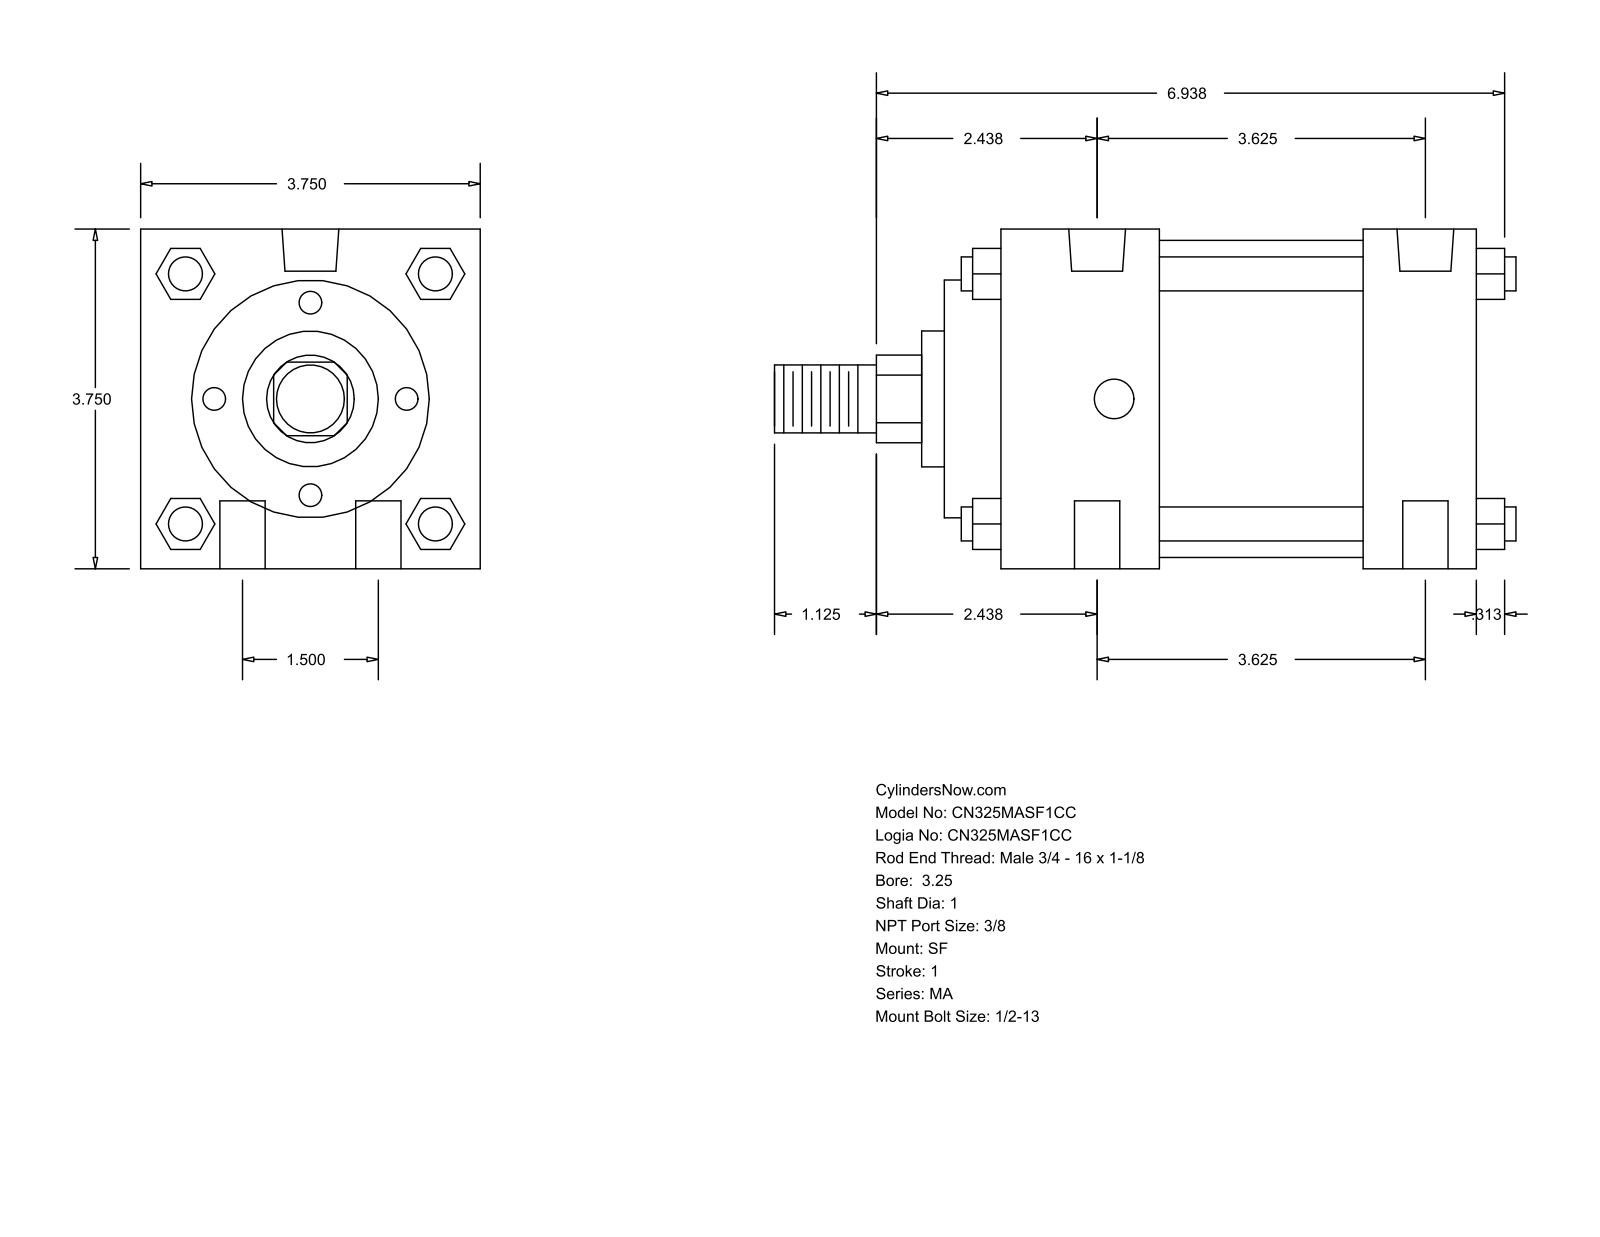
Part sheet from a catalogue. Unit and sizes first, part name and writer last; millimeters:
Units: millimetres
Overall size (bounding box): 207.96 × 95.25 × 95.25
Round holes (diameter × count): ⌀12.7 ×4, ⌀11.11 ×2, ⌀15.93 ×2
Round bosses / shafts (diameter × count): ⌀9.53 ×4, ⌀88.9 ×1, ⌀66.67 ×1, ⌀38.1 ×1, ⌀25.4 ×1, ⌀19.05 ×1
Partial cylindrical surfaces — rounded edges, fillets, slot ends (radius × count): R12.29 ×1
Main face-to-face distances: 95.24, 133.36, 101.61, 31.75, 44.46, 57.15, 88.9, 15.87, 60.33, 117.48
Hole centre spacings: 19.05, 94.03, 92.08, 38.1, 99.65, 82.55
Bodies: 0 solids, 126 faces (95 planar, 31 cylindrical, 0 other)
Part name (STEP PRODUCT): MA_SF__0325_1
STEP written by: GSSL Pune (CONFIG_CONTROL_DESIGN)
